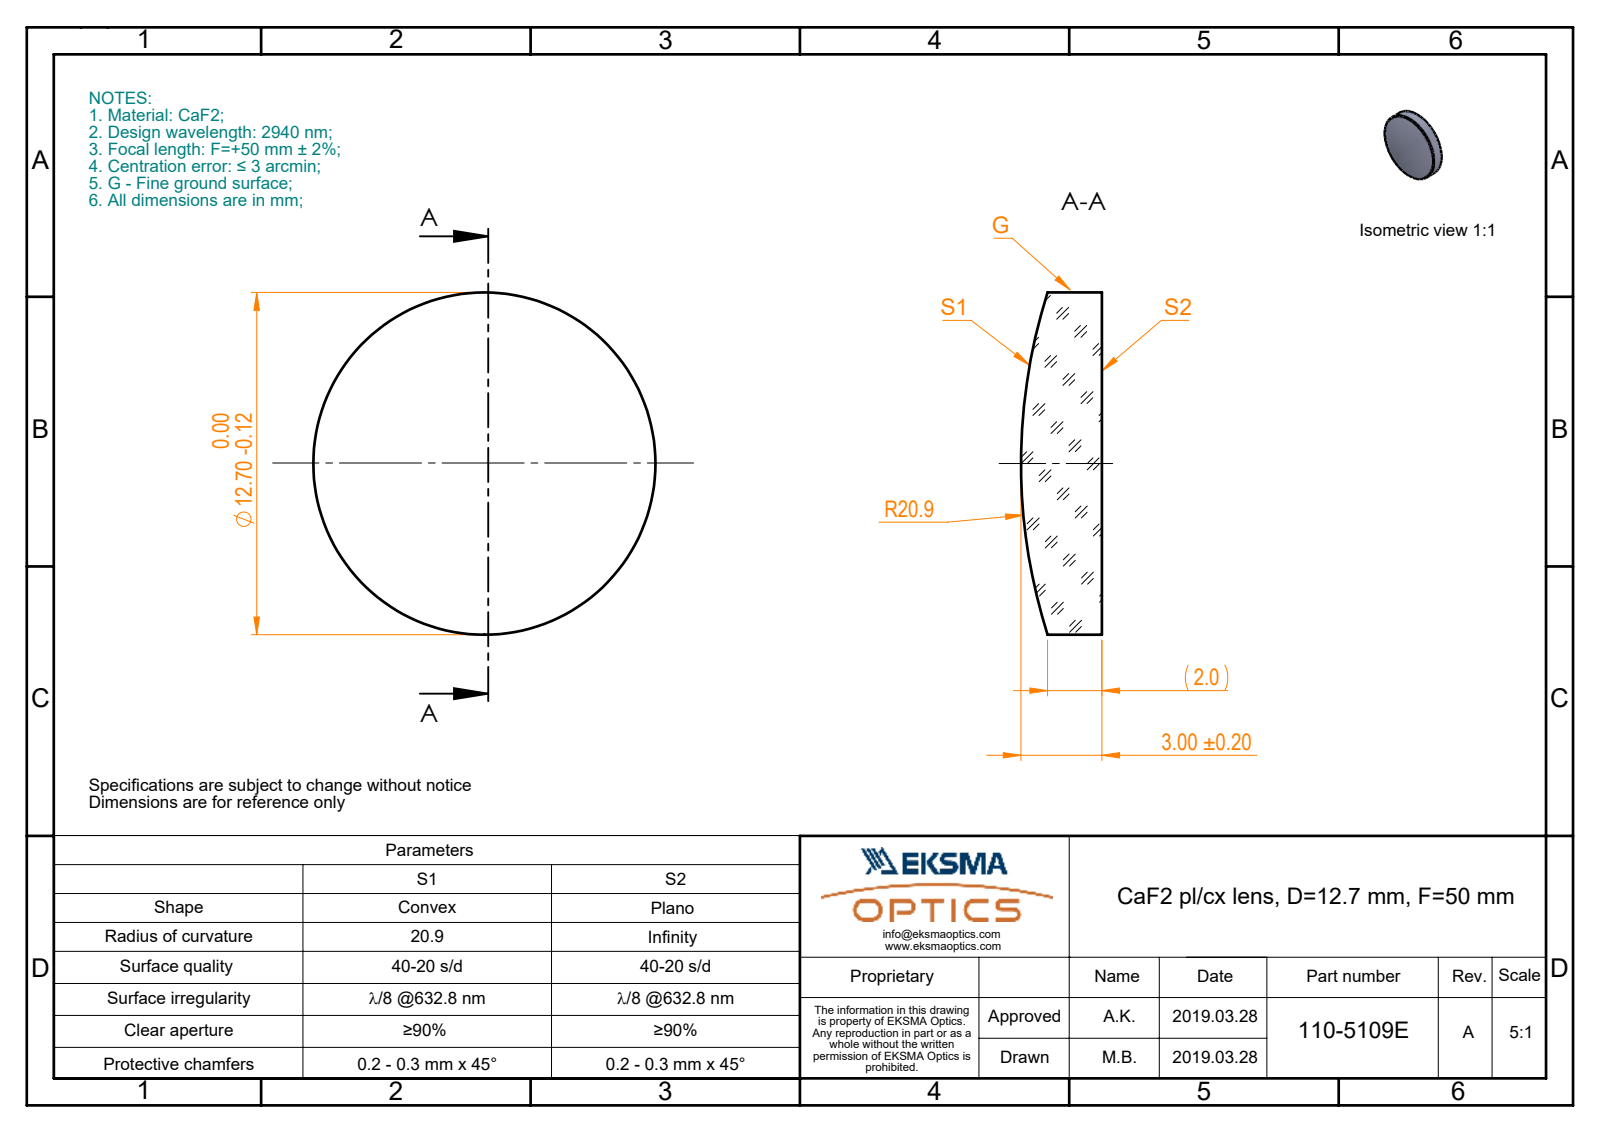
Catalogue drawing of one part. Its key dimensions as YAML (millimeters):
part_name: "110-5109E CaF2 pl-cx 12.7 F50"
step_written_by: "SolidWorks 2017 (CONFIG_CONTROL_DESIGN)"
units: millimeters
bodies: {solids: 1, faces: 5, planar: 1, cylindrical: 2, other: 2}
overall_size: [12.7, 12.7, 3]
volume: 318
surface_area: 337
round_bosses_or_shafts:
  - {diameter: 12.7, count: 1}
